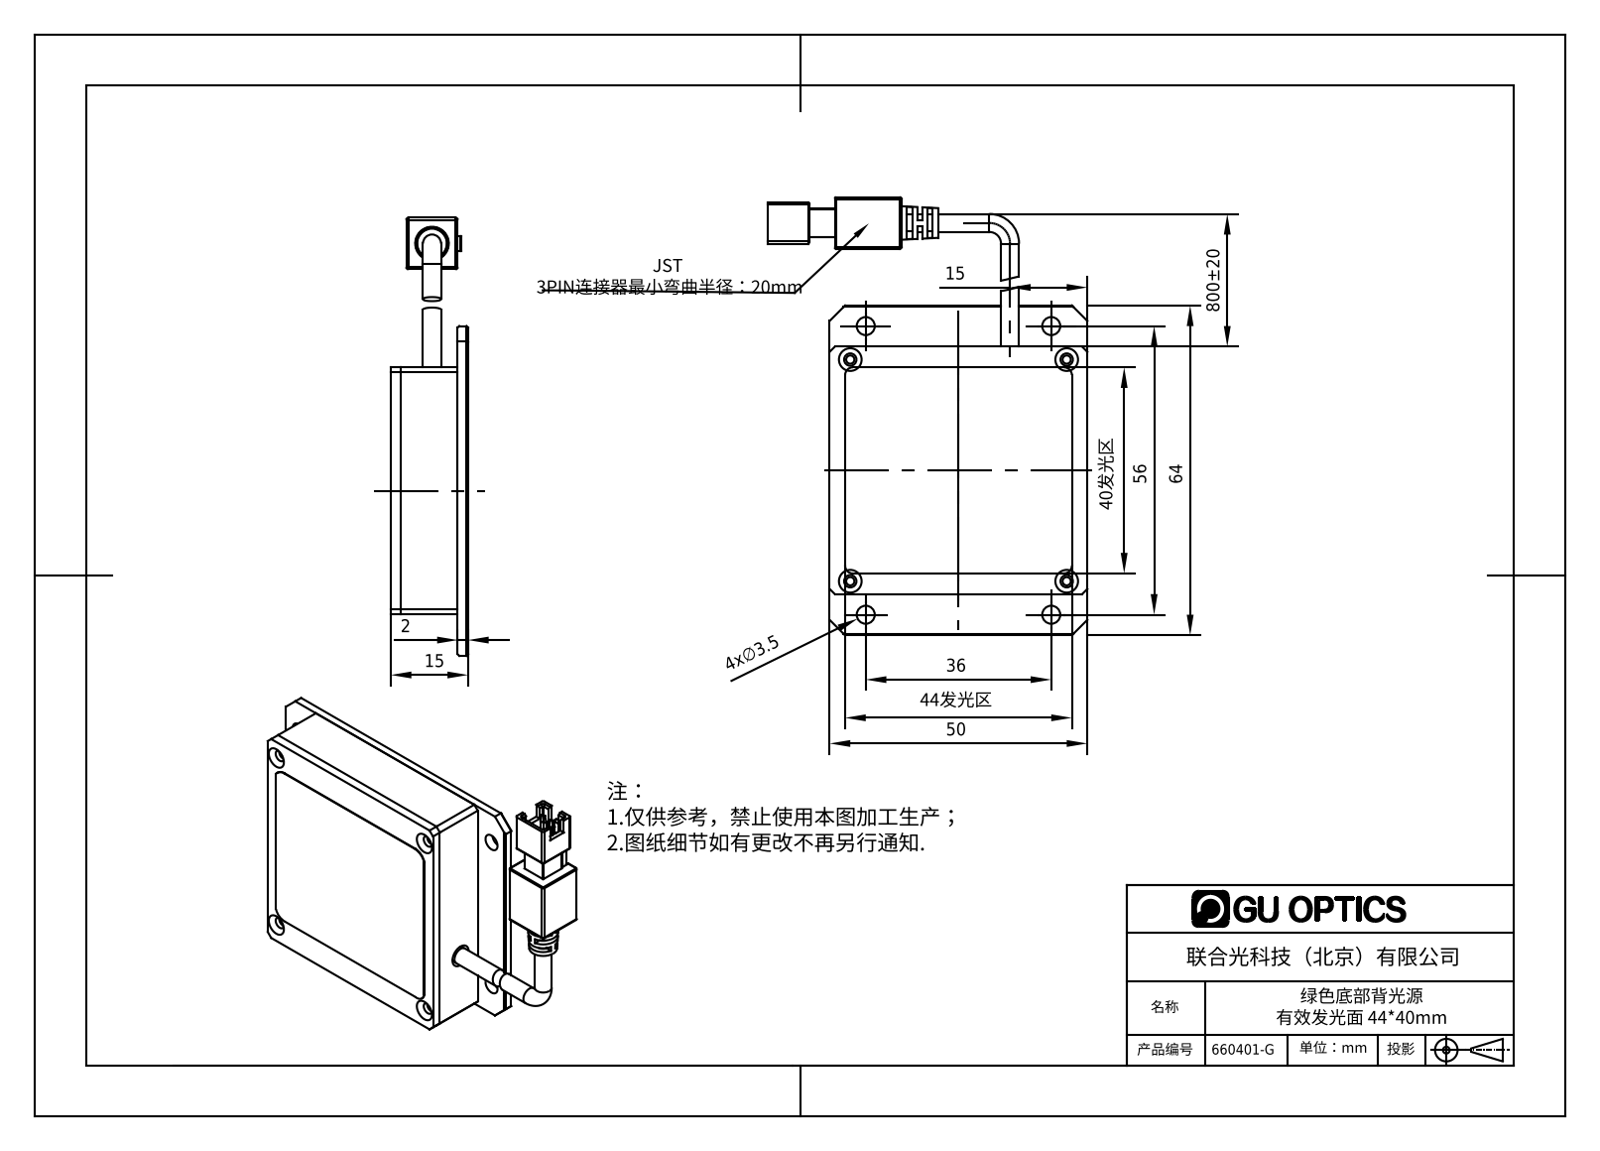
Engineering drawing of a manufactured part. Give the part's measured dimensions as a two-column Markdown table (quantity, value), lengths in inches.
| quantity | value |
| --- | --- |
| part name | 660401-G |
| STEP written by | SolidWorks 2016 (AUTOMOTIVE_DESIGN) |
| units | inches |
| bodies | 6 solids, 476 faces (239 planar, 118 cylindrical, 119 other) |
| overall size | 3.346 × 2.441 × 0.594 |
| volume | 1.326 in³ |
| surface area | 36.46 in² |
| round holes (diameter × count) | 0.063 × 8, 0.094 × 8, 0.138 × 4 |
| round bosses / shafts (diameter × count) | 0.138 × 2 |
| partial cylindrical surfaces (radius × count) | 0.004 × 15, 0.008 × 13, 0.016 × 12, 0.059 × 6, 0.039 × 4, 0.012 × 1, 0.027 × 1, 0.055 × 1 |
| main face-to-face distances | 0.079, 0.512, 0.433, 0.118, 0.039, 0.394, 0.083, 0.476, 0.594, 0.516 |
| hole center spacings | 0.039, 0.246, 0.282, 1.551, 1.557, 1.654, 1.654, 1.732 |
